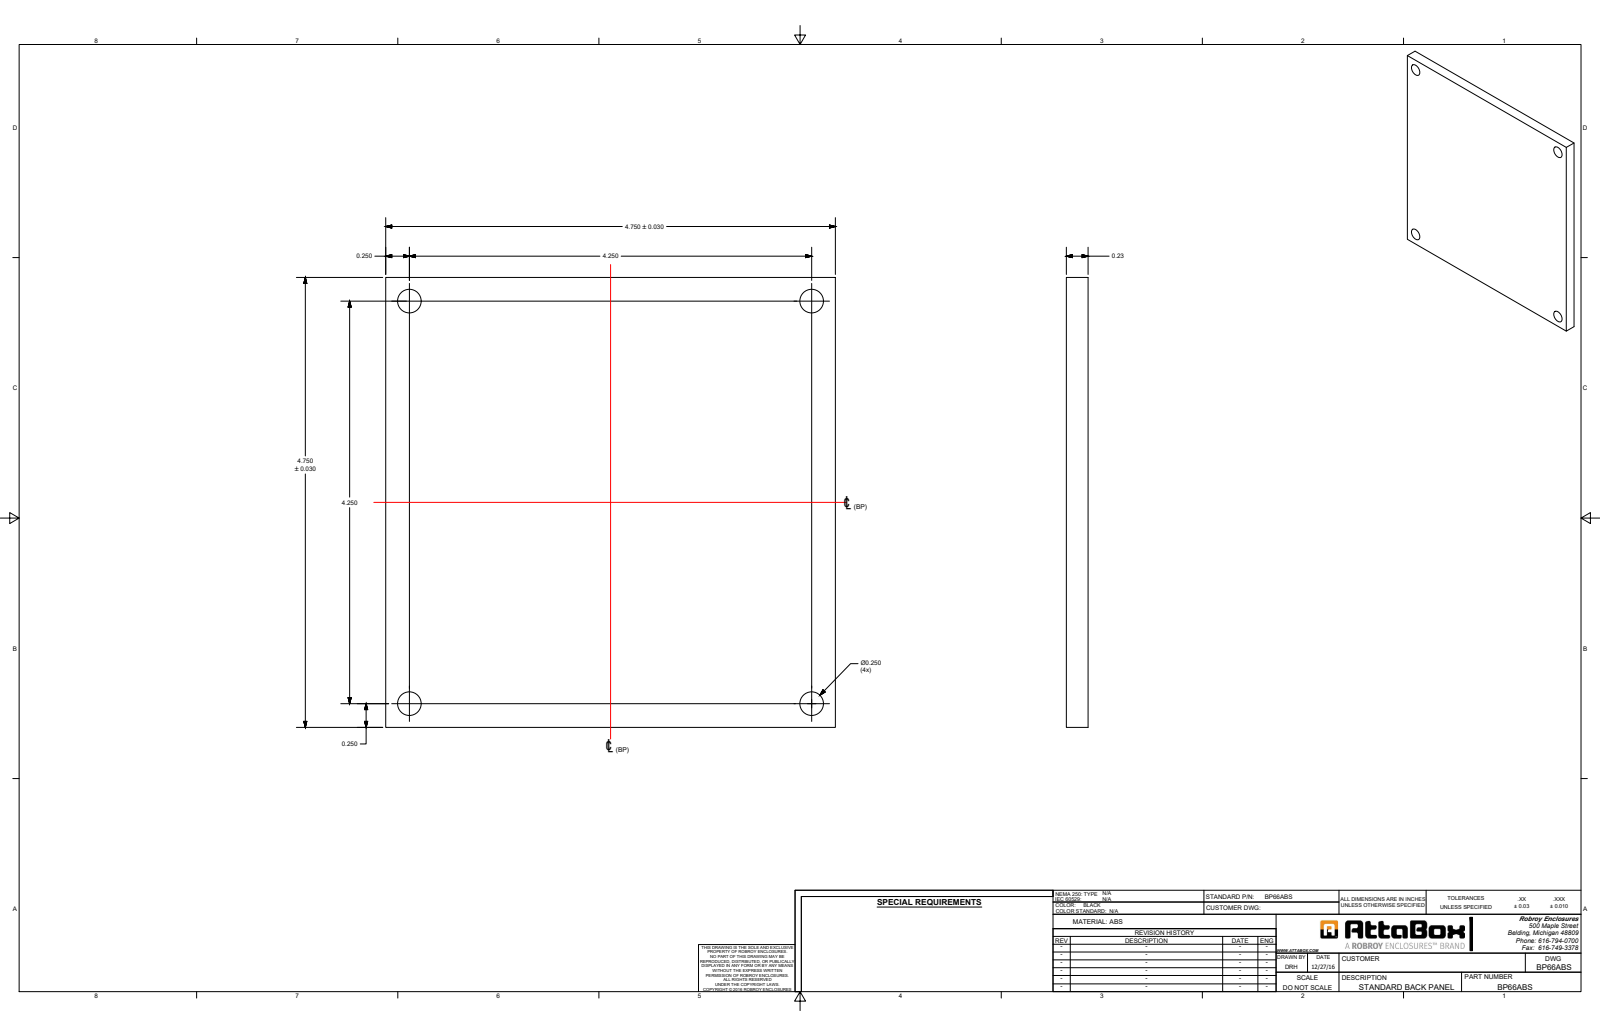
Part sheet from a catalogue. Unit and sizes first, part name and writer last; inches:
Units: inches
Overall size (bounding box): 4.75 × 4.75 × 0.23
Round holes (diameter × count): ⌀0.25 ×4
Main face-to-face distances: 0.23, 4.75
Hole centre spacings: 4.25, 6.01
Volume: 5.144 in³ · Surface area: 49.82 in²
Bodies: 1 solid, 10 faces (6 planar, 4 cylindrical, 0 other)
Part name (STEP PRODUCT): BP66ABS
STEP written by: SolidWorks 2023 (AUTOMOTIVE_DESIGN)
